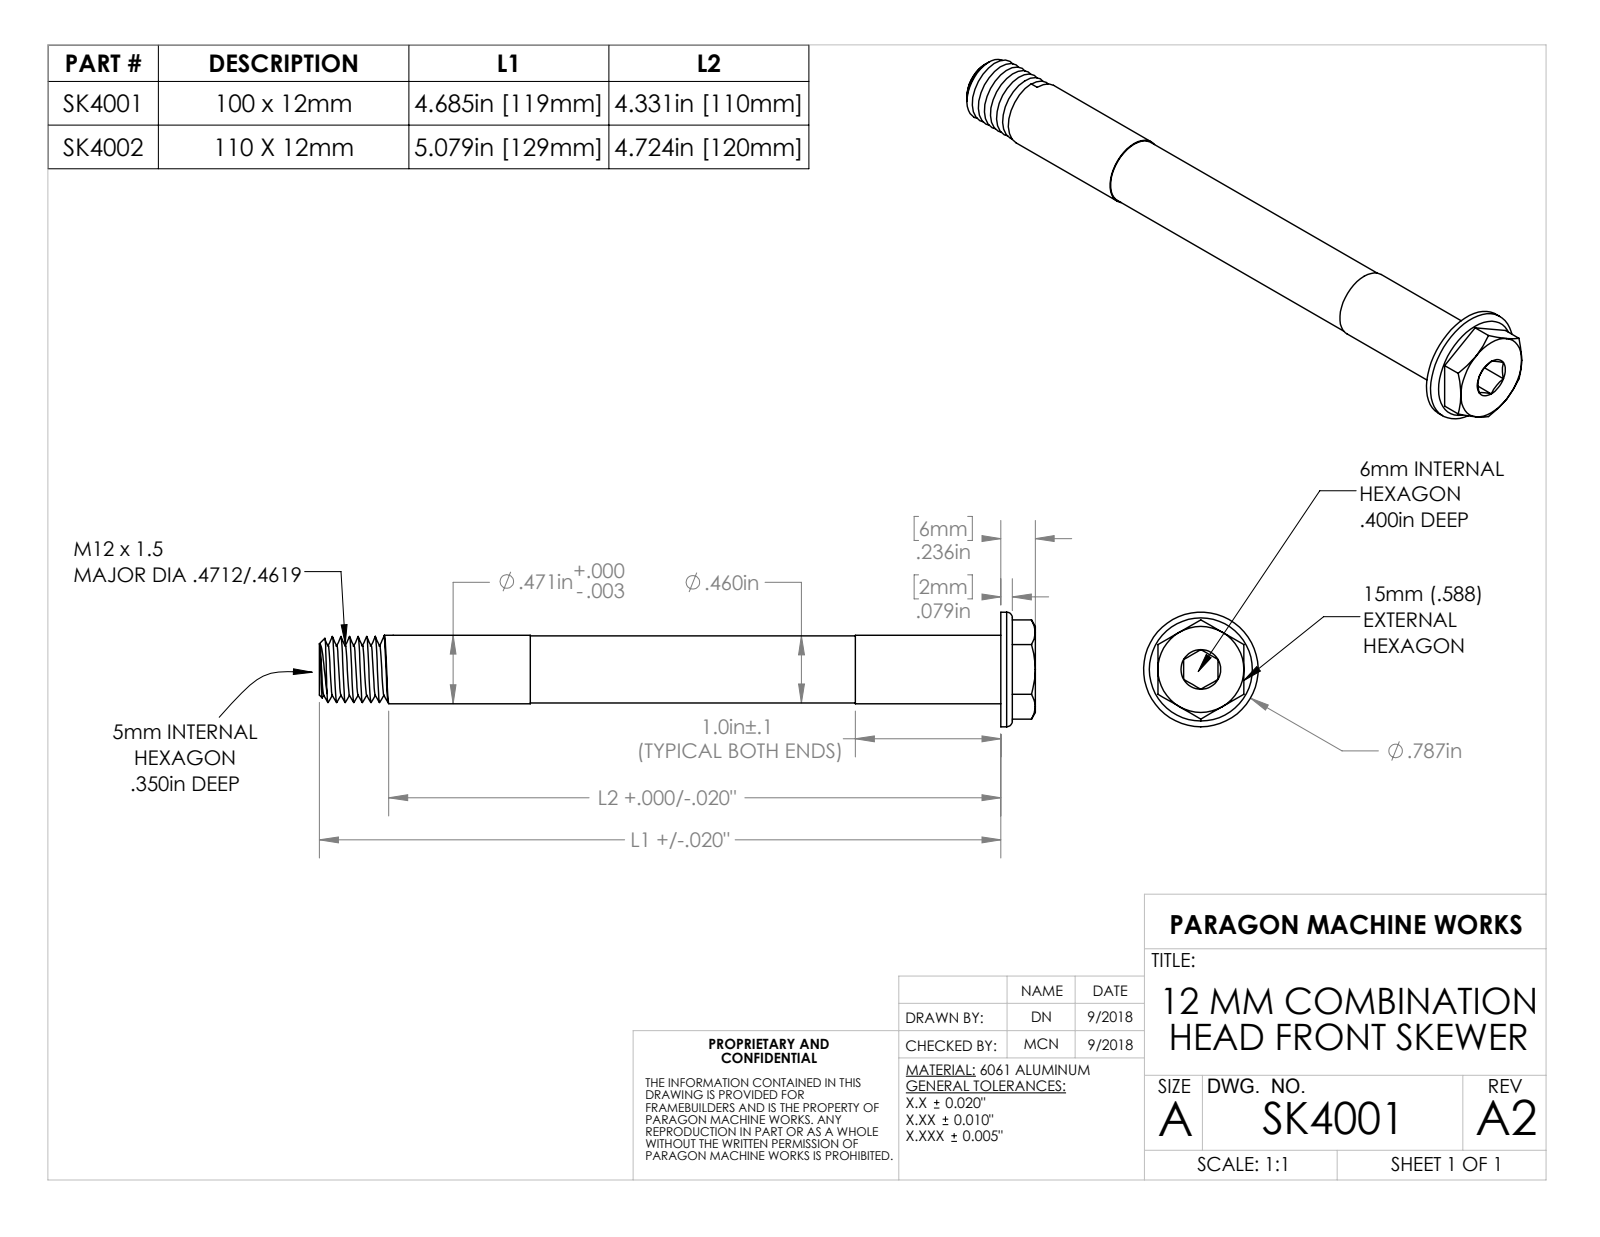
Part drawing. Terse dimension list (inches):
name: SK4001
written by: SolidWorks 2015 (AUTOMOTIVE_DESIGN)
unit: in
bodies: 1 solid, 48 faces (20 planar, 8 cylindrical, 20 other)
size: 4.921 × 0.787 × 0.787
volume: 0.851 in³; area: 8.877 in²
bosses: 1× ⌀0.787, 1× ⌀0.471, 1× ⌀0.46
face distances: 0.236, 0.177, 0.413, 0.591, 4.685, 4.921, 0.039, 4.764, 0.079, 0.157
